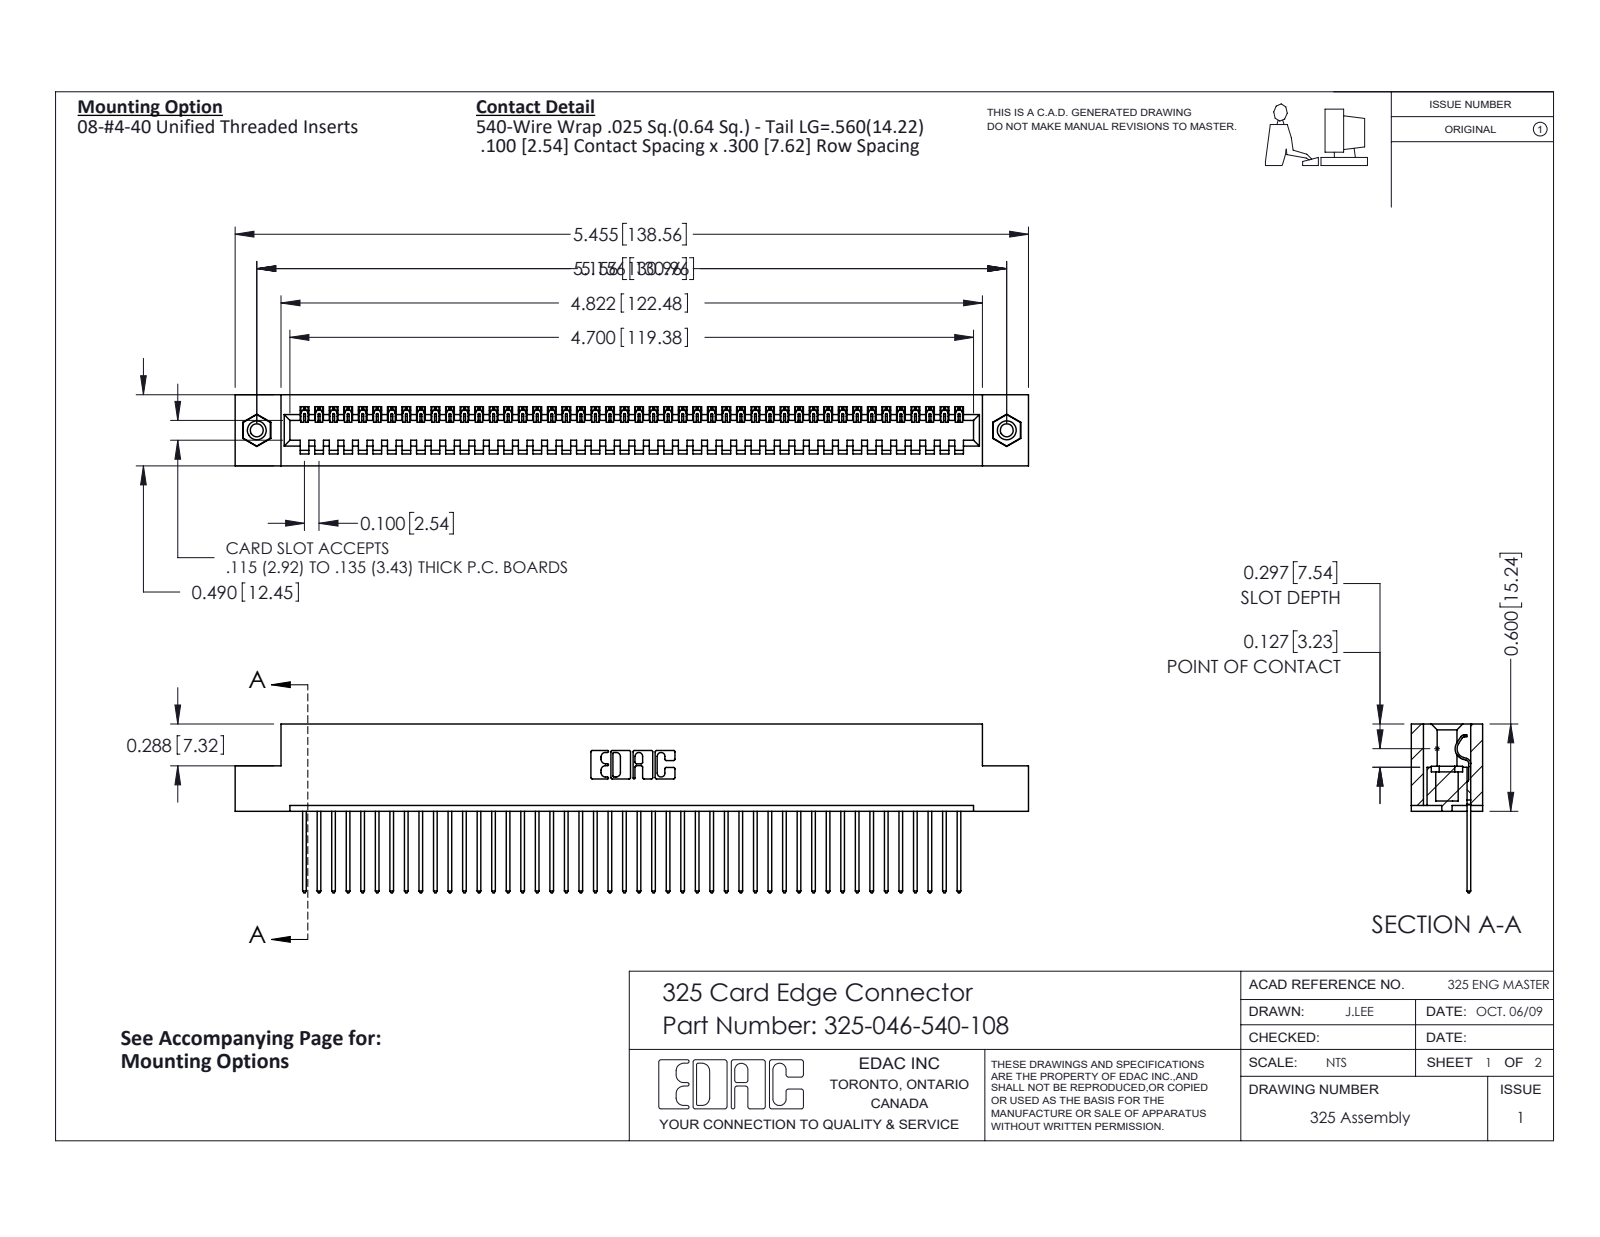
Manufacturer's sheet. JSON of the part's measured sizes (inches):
{"part_name": "345-250-001_345-250-003-102; 325-046-540-108; 325 Part_TI; 325-292-001_325-293-140", "step_written_by": "SolidWorks 2016 (CONFIG_CONTROL_DESIGN)", "units": "inches", "bodies": {"solids": 49, "faces": 2842, "planar": 2034, "cylindrical": 792, "other": 16}, "overall_size": [5.455, 1.16, 0.49], "volume_in3": 1.079, "surface_area_in2": 30.78, "round_holes": [[0.089, 2], [0.125, 2], [0.16, 2]], "round_bosses_or_shafts": [[0.155, 2]], "partial_cylinders_radius": [[0.006, 92], [0.01, 92], [0.01, 22], [0.007, 6], [0.031, 6], [0.026, 3], [0.014, 1], [0.022, 1]], "face_to_face_distances": [0.083, 0.407, 0.49, 0.3, 0.107, 0.383, 0.025, 0.325, 0.56, 0.263], "hole_center_spacings": [5.156]}
